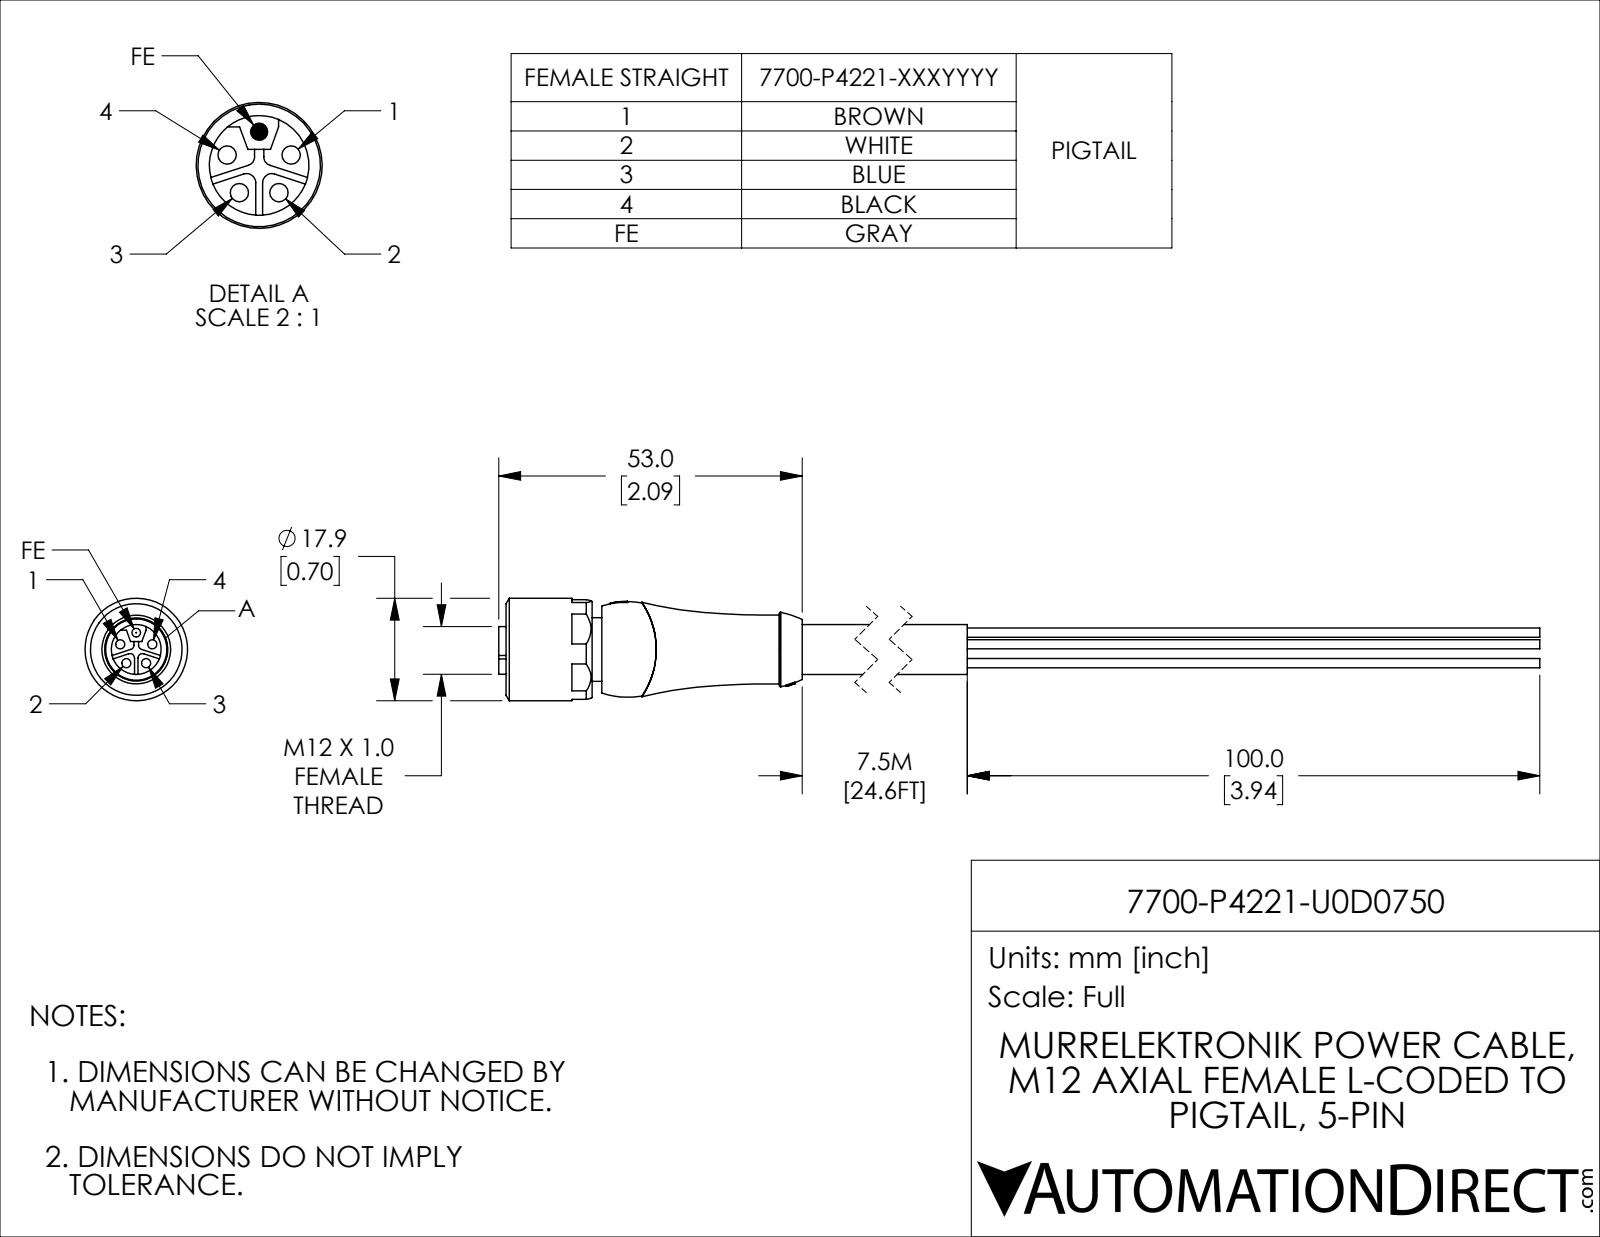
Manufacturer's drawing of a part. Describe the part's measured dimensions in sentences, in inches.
The part is named "7700-P4221-U0D0750". Its 3-D file was written by "SolidWorks 2021 (CONFIG_CONTROL_DESIGN)". It is 2 solids with 142 faces: 69 planar, 40 cylindrical and 33 other. Overall it measures 7.598 by 0.705 by 0.705 inches. Its volume is 0.735 cubic inches and its surface area 12.83 square inches. Round holes: 4 of diameter 0.063, 1 of diameter 0.433, 1 of diameter 0.512. Round bosses or shafts: 1 of diameter 0.705, 1 of diameter 0.51, 1 of diameter 0.437, 1 of diameter 0.343, 1 of diameter 0.063, 1 of diameter 0.059. Partial cylindrical surfaces (rounded edges, fillets, slot ends): 4 of radius 0.031. The main face-to-face distances are 0.657, 0.591, 0.067, 0.667, 3.61, 3.02, 2.953, 0.181, 0.362, 0.228. The hole center spacings are 0.116, 0.136, 0.22.
